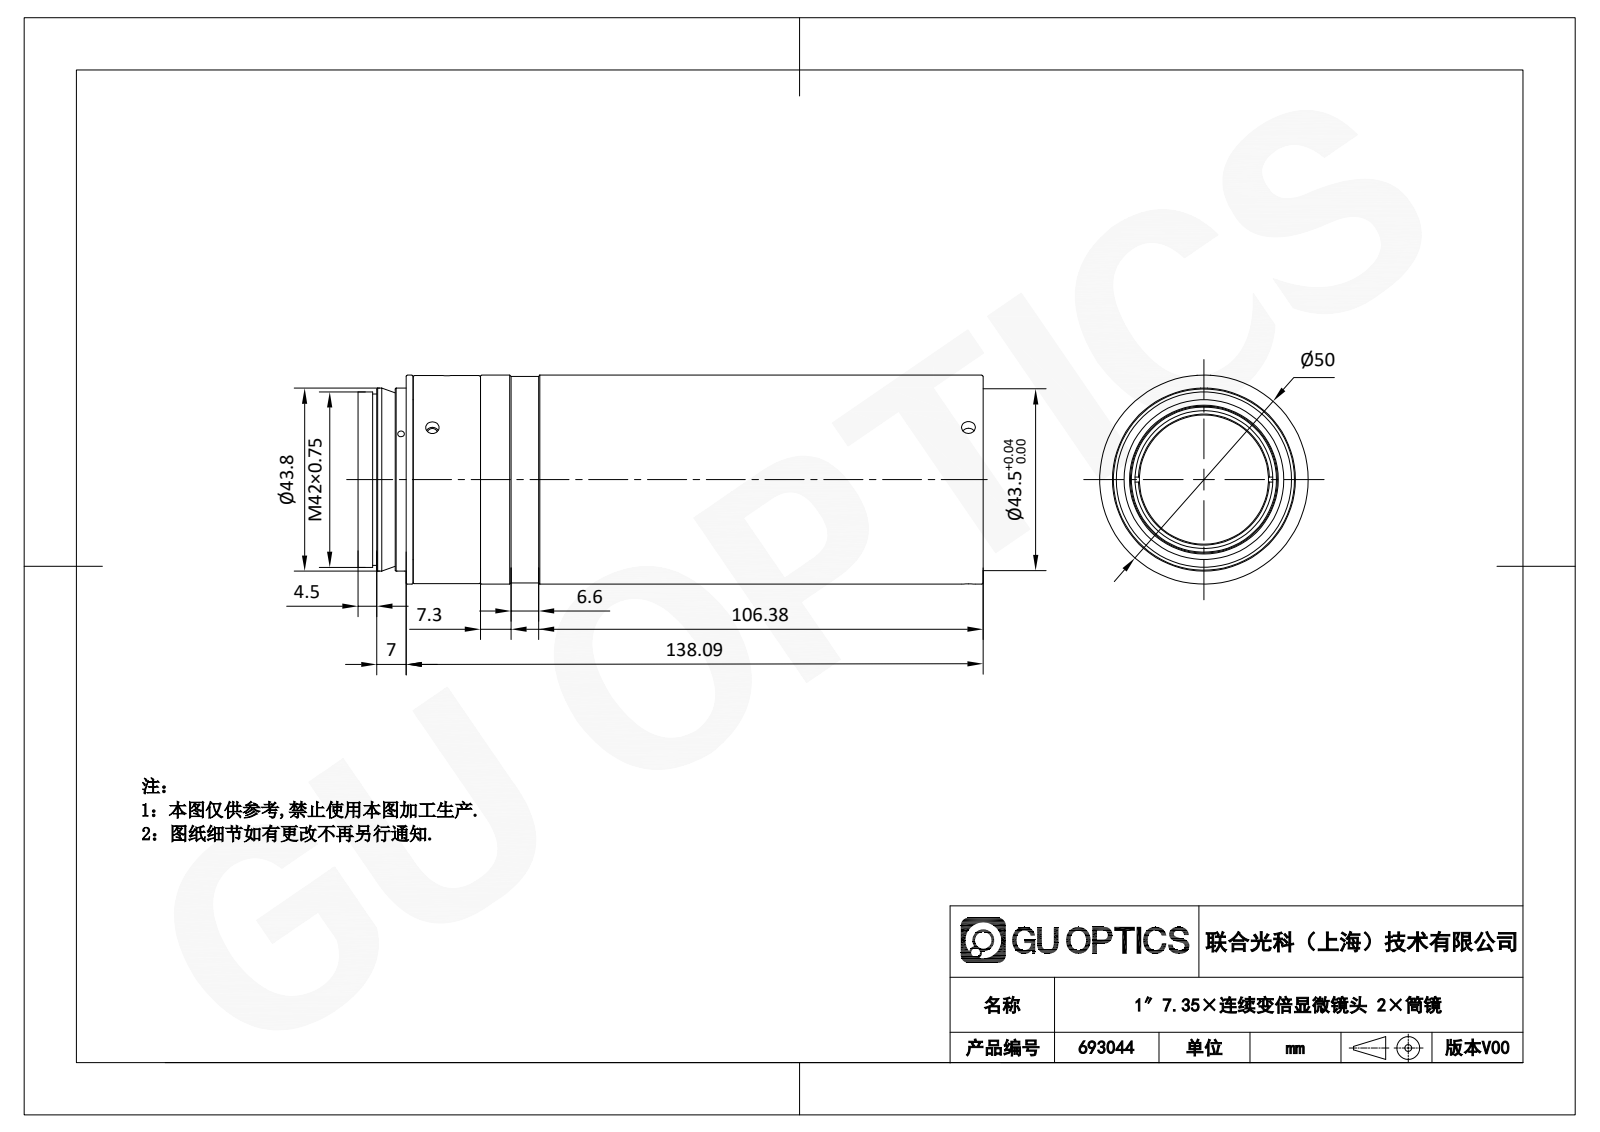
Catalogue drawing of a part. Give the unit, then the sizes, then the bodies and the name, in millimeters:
Units: millimetres
Overall size (bounding box): 149.59 × 50 × 50
Round holes (diameter × count): ⌀3.3 ×3, ⌀2.5 ×2, ⌀3.2 ×2, ⌀2.7 ×1, ⌀32 ×1, ⌀41 ×1, ⌀42 ×1, ⌀43.5 ×1, ⌀43.8 ×1
Round bosses / shafts (diameter × count): ⌀1.6 ×3, ⌀50 ×1, ⌀49.8 ×1, ⌀49.4 ×1, ⌀44.6 ×1, ⌀38.25 ×1, ⌀35.2 ×1, ⌀33 ×1
Main face-to-face distances: 124.6, 127.09, 2.49, 11, 135.6, 138.09, 22.88, 11.88, 112.72, 115.21
Hole centre spacings: 128.29, 124.84
Bodies: 0 solids, 117 faces (42 planar, 31 cylindrical, 44 other)
Part name (STEP PRODUCT): 693044
STEP written by: SolidWorks 2020 (CONFIG_CONTROL_DESIGN)
